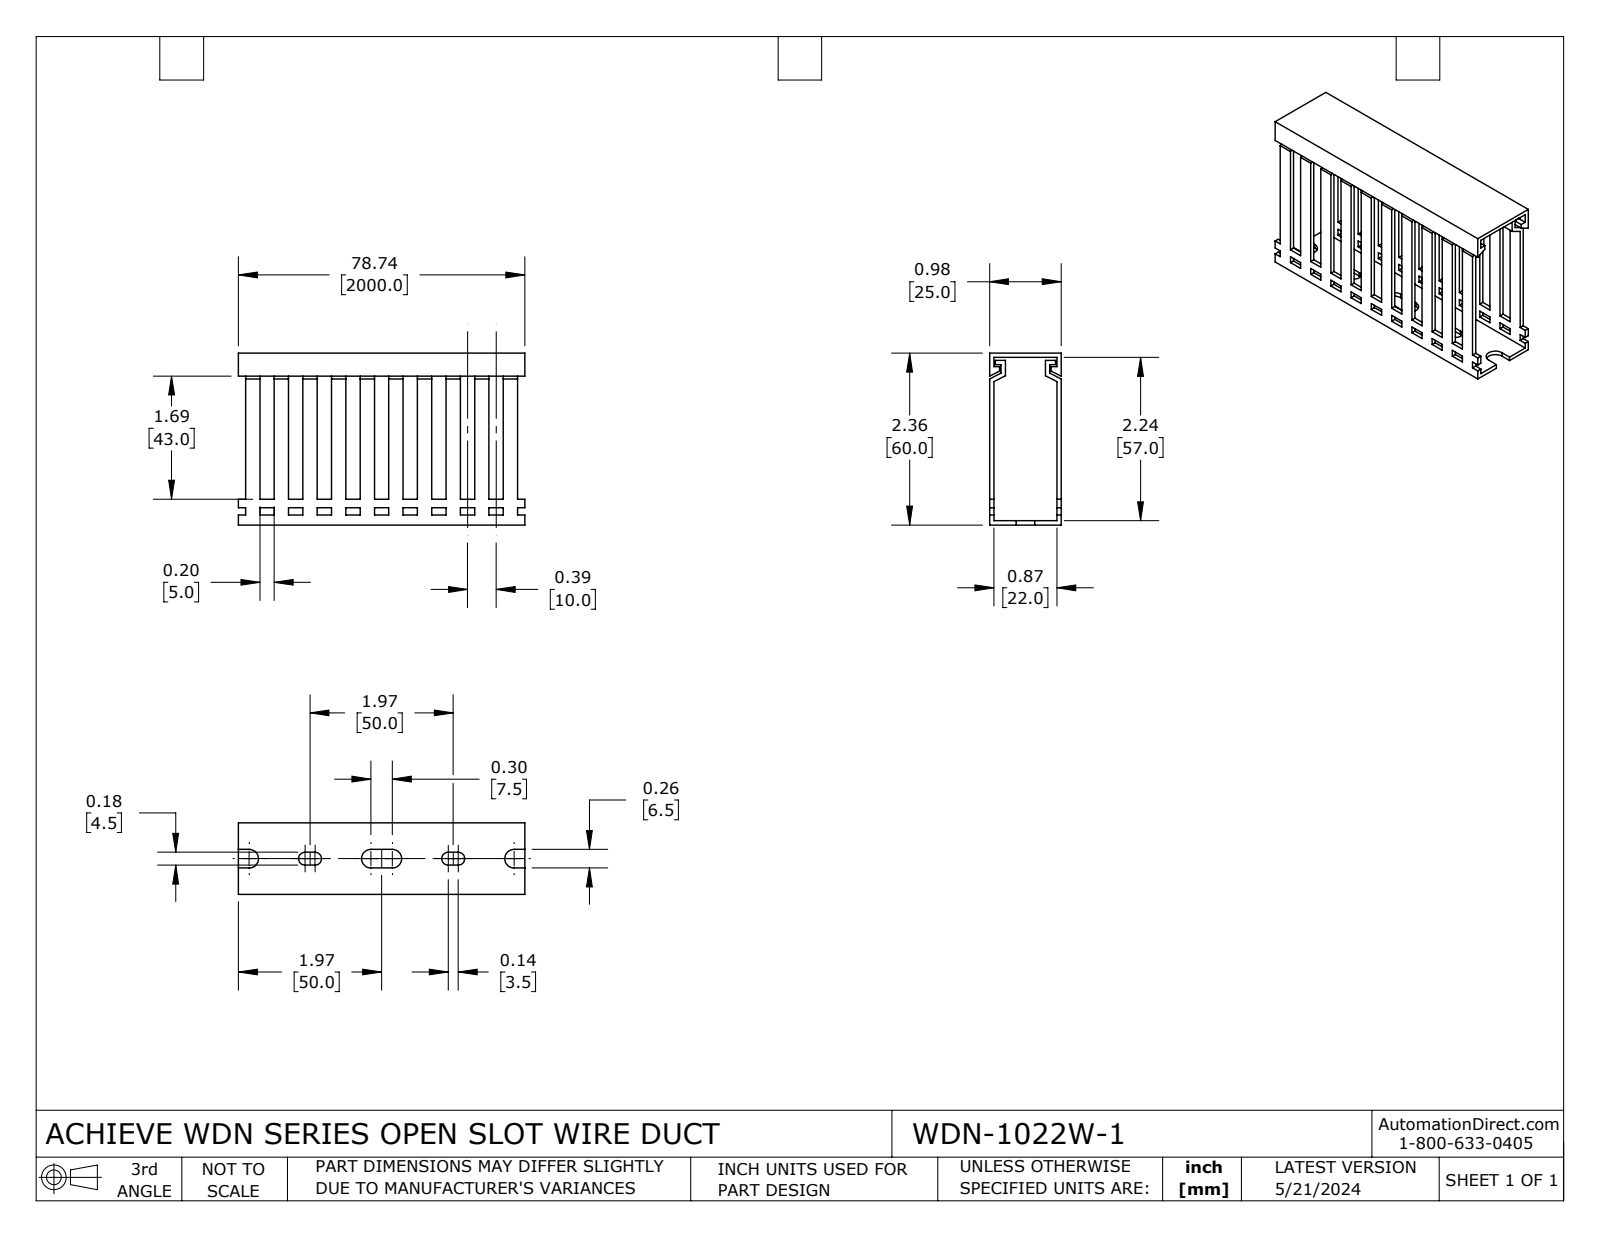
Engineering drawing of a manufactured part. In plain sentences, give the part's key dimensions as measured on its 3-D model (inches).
The part is named "WDN-1022W-1". Its 3-D file was written by "SolidWorks 2023 (CONFIG_CONTROL_DESIGN)". It is 2 solids with 336 faces: 324 planar, 12 cylindrical and 0 other. Overall it measures 3.937 by 2.362 by 0.984 inches. Its volume is 1.197 cubic inches and its surface area 47.1 square inches. Partial cylindrical surfaces (rounded edges, fillets, slot ends): 4 of radius 0.089, 4 of radius 0.128. The main face-to-face distances are 0.059, 0.984, 0.925, 2.303, 2.362, 0.197, 0.866, 0.394, 0.787, 0.591.
